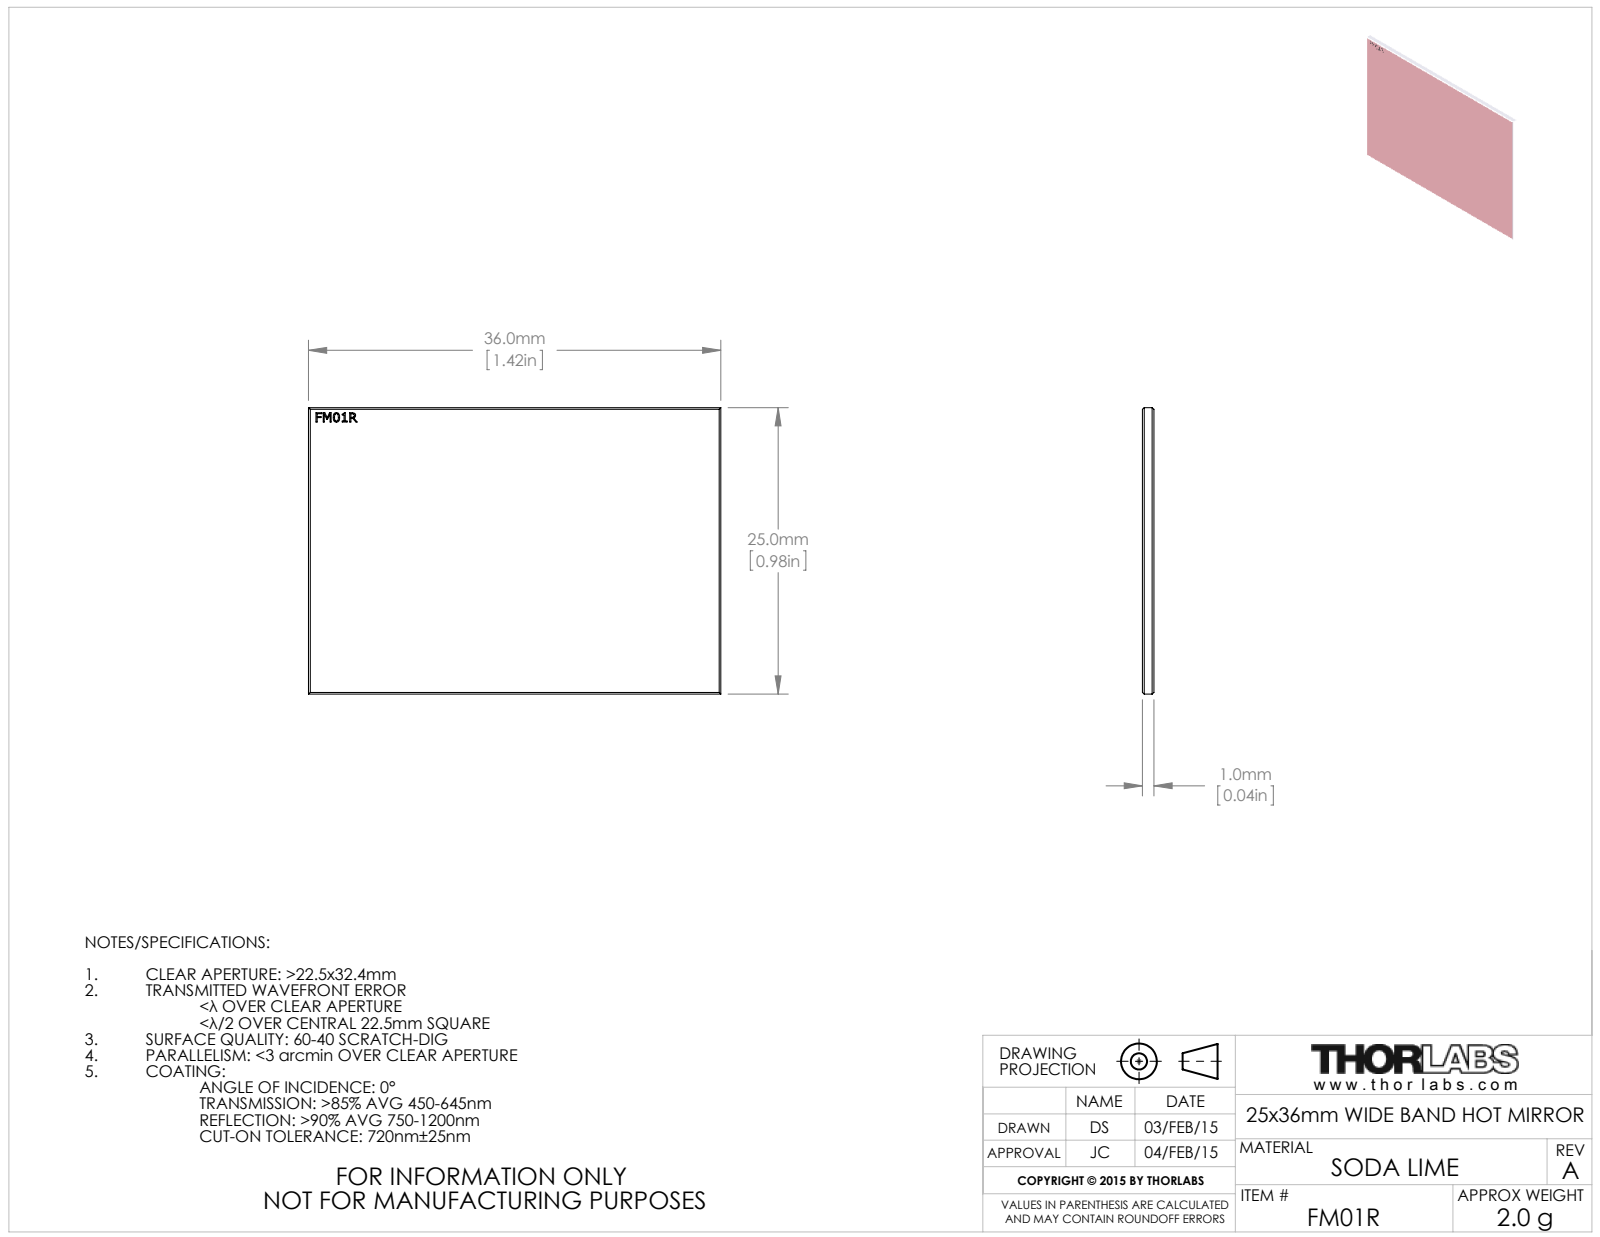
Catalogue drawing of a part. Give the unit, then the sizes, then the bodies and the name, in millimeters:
Units: millimetres
Overall size (bounding box): 36 × 25 × 1
Main face-to-face distances: 1, 25, 36, 18.16, 25.94
Volume: 897 mm³ · Surface area: 1 900 mm²
Bodies: 1 solid, 21 faces (21 planar, 0 cylindrical, 0 other)
Part name (STEP PRODUCT): TTN034987-E0W
STEP written by: SolidWorks 2014 (CONFIG_CONTROL_DESIGN)
